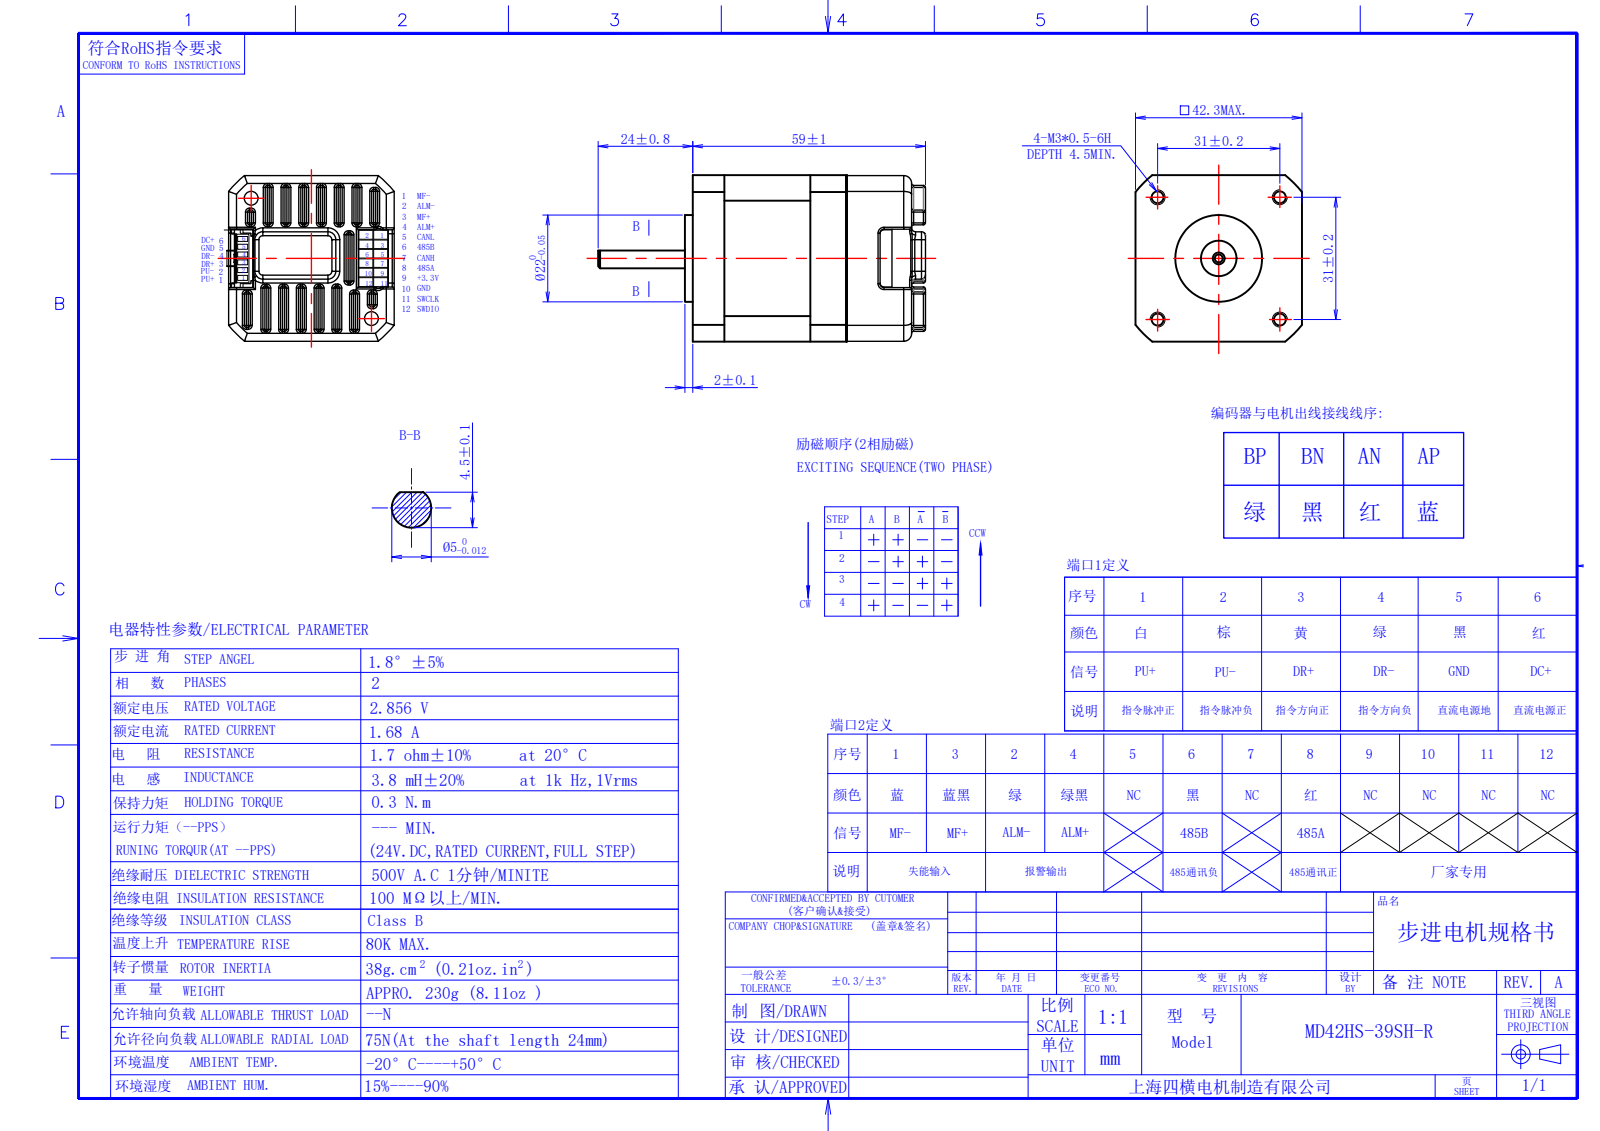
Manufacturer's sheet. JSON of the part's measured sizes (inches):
{"part_name": "01.B013.000060 42BH新款编码器后罩; 42板子; 42H239-L66mm; HX20028-12A.stp (+8 more)", "step_written_by": "SolidWorks 2022 (CONFIG_CONTROL_DESIGN)", "units": "inches", "bodies": {"solids": 13, "faces": 1758, "planar": 932, "cylindrical": 545, "other": 281}, "overall_size": [3.268, 1.665, 1.665], "volume_in3": 4.496, "surface_area_in2": 58.69, "round_holes": [[0.098, 6], [0.13, 4], [0.138, 4], [0.217, 4], [0.041, 2], [0.059, 2], [0.069, 2], [0.122, 2], [0.177, 2], [0.079, 1], [0.236, 1], [0.354, 1]], "round_bosses_or_shafts": [[0.197, 5], [0.118, 4], [0.083, 2], [1.02, 1], [0.866, 1], [0.315, 1]], "partial_cylinders_radius": [[0.02, 174], [0.059, 37], [0.039, 24], [0.016, 8], [0.017, 8], [0.079, 8], [0.012, 4], [0.033, 2]], "face_to_face_distances": [1.535, 0.315, 0.866, 1.665, 0.354, 0.059, 1.22, 1.659, 0.669, 1.181], "hole_center_spacings": [1.211, 0.014, 0.056, 0.057, 0.674, 0.687, 0.706, 0.849]}
